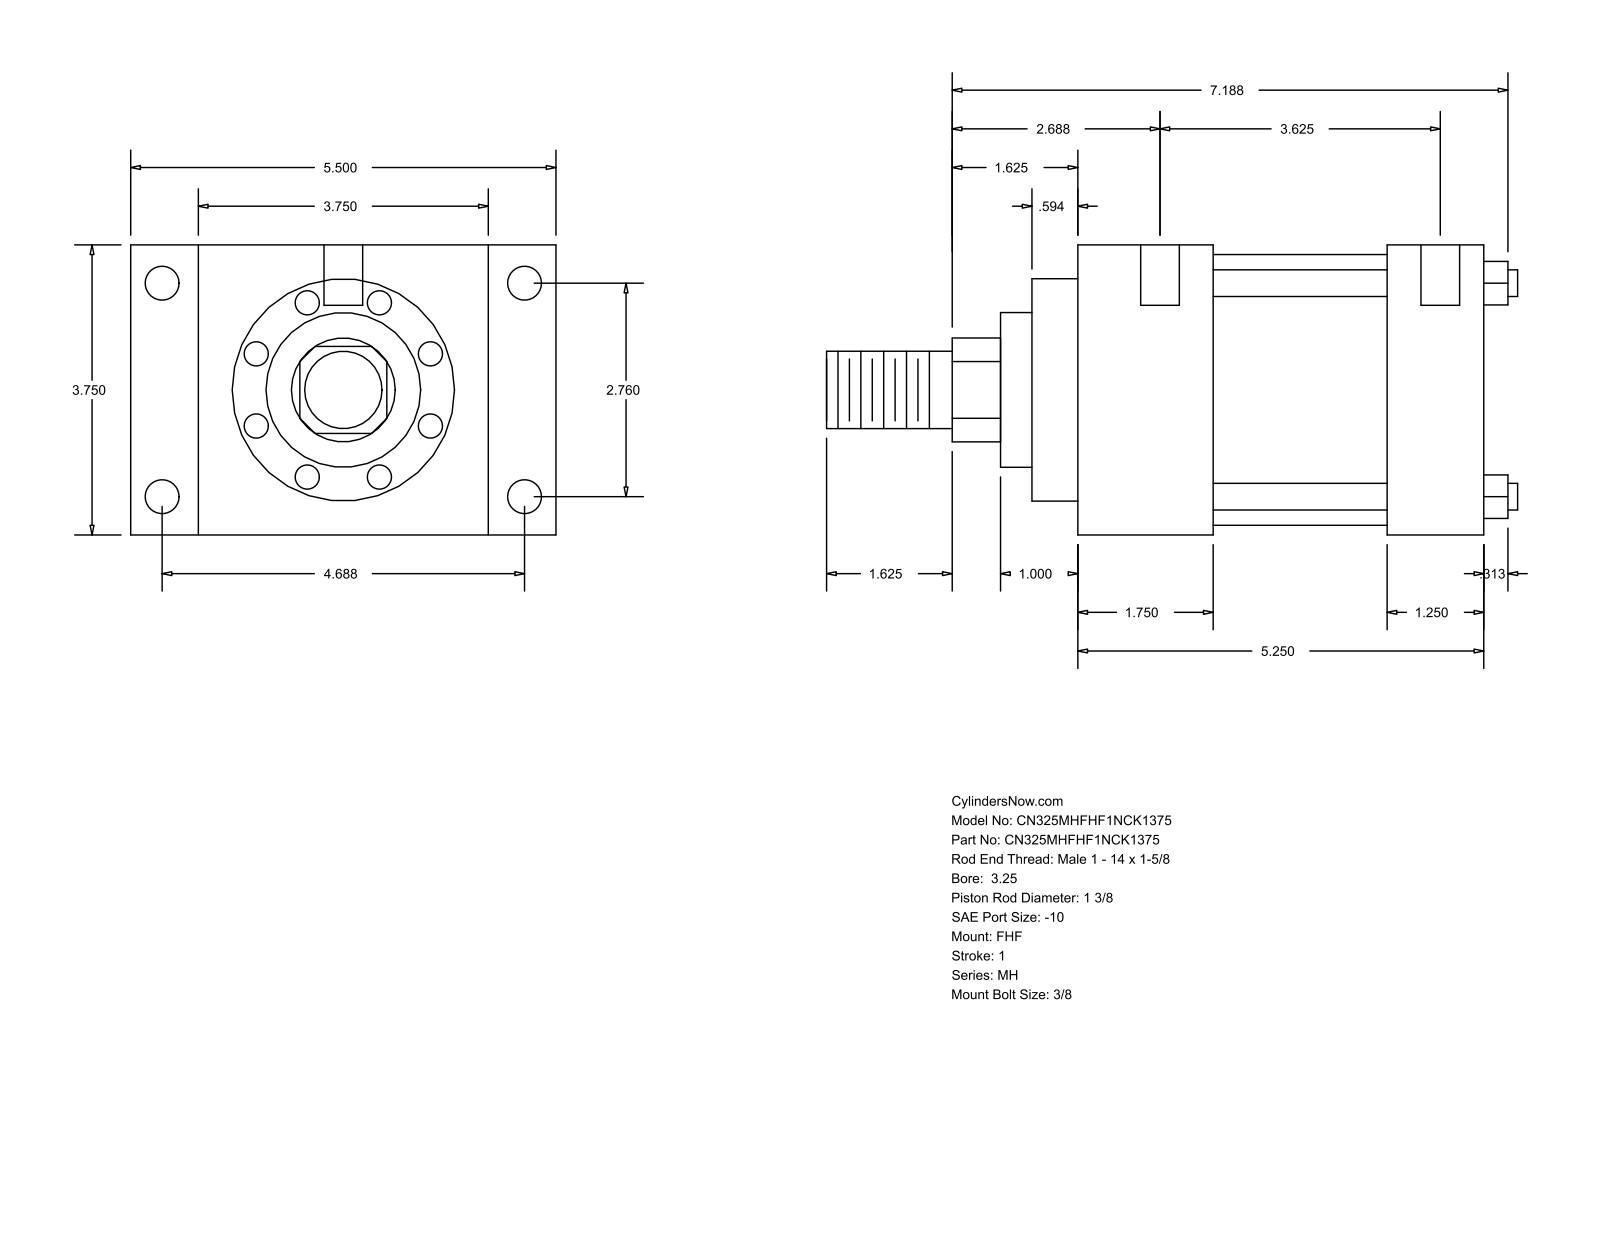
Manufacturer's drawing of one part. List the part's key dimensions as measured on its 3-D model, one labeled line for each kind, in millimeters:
Part name (STEP PRODUCT): MH_FHF__0325_1.375
STEP written by: GSSL Pune (CONFIG_CONTROL_DESIGN)
Units: millimetres
Bodies: 0 solids, 90 faces (61 planar, 29 cylindrical, 0 other)
Overall size (bounding box): 227.01 × 139.7 × 95.25
Round holes (diameter × count): ⌀5.56 ×4, ⌀11.13 ×4, ⌀12.7 ×2
Round bosses / shafts (diameter × count): ⌀8.76 ×4, ⌀88.9 ×1, ⌀73.03 ×1, ⌀50.8 ×1, ⌀34.92 ×1, ⌀25.4 ×1
Partial cylindrical surfaces — rounded edges, fillets, slot ends (radius × count): R17.06 ×1
Main face-to-face distances: 95.24, 133.35, 44.45, 88.9, 22.23, 117.47, 139.7, 101.61, 57.16, 31.74
Hole centre spacings: 70.1, 98.43, 119.06, 138.16, 1.59, 4.76, 92.08, 93.67
